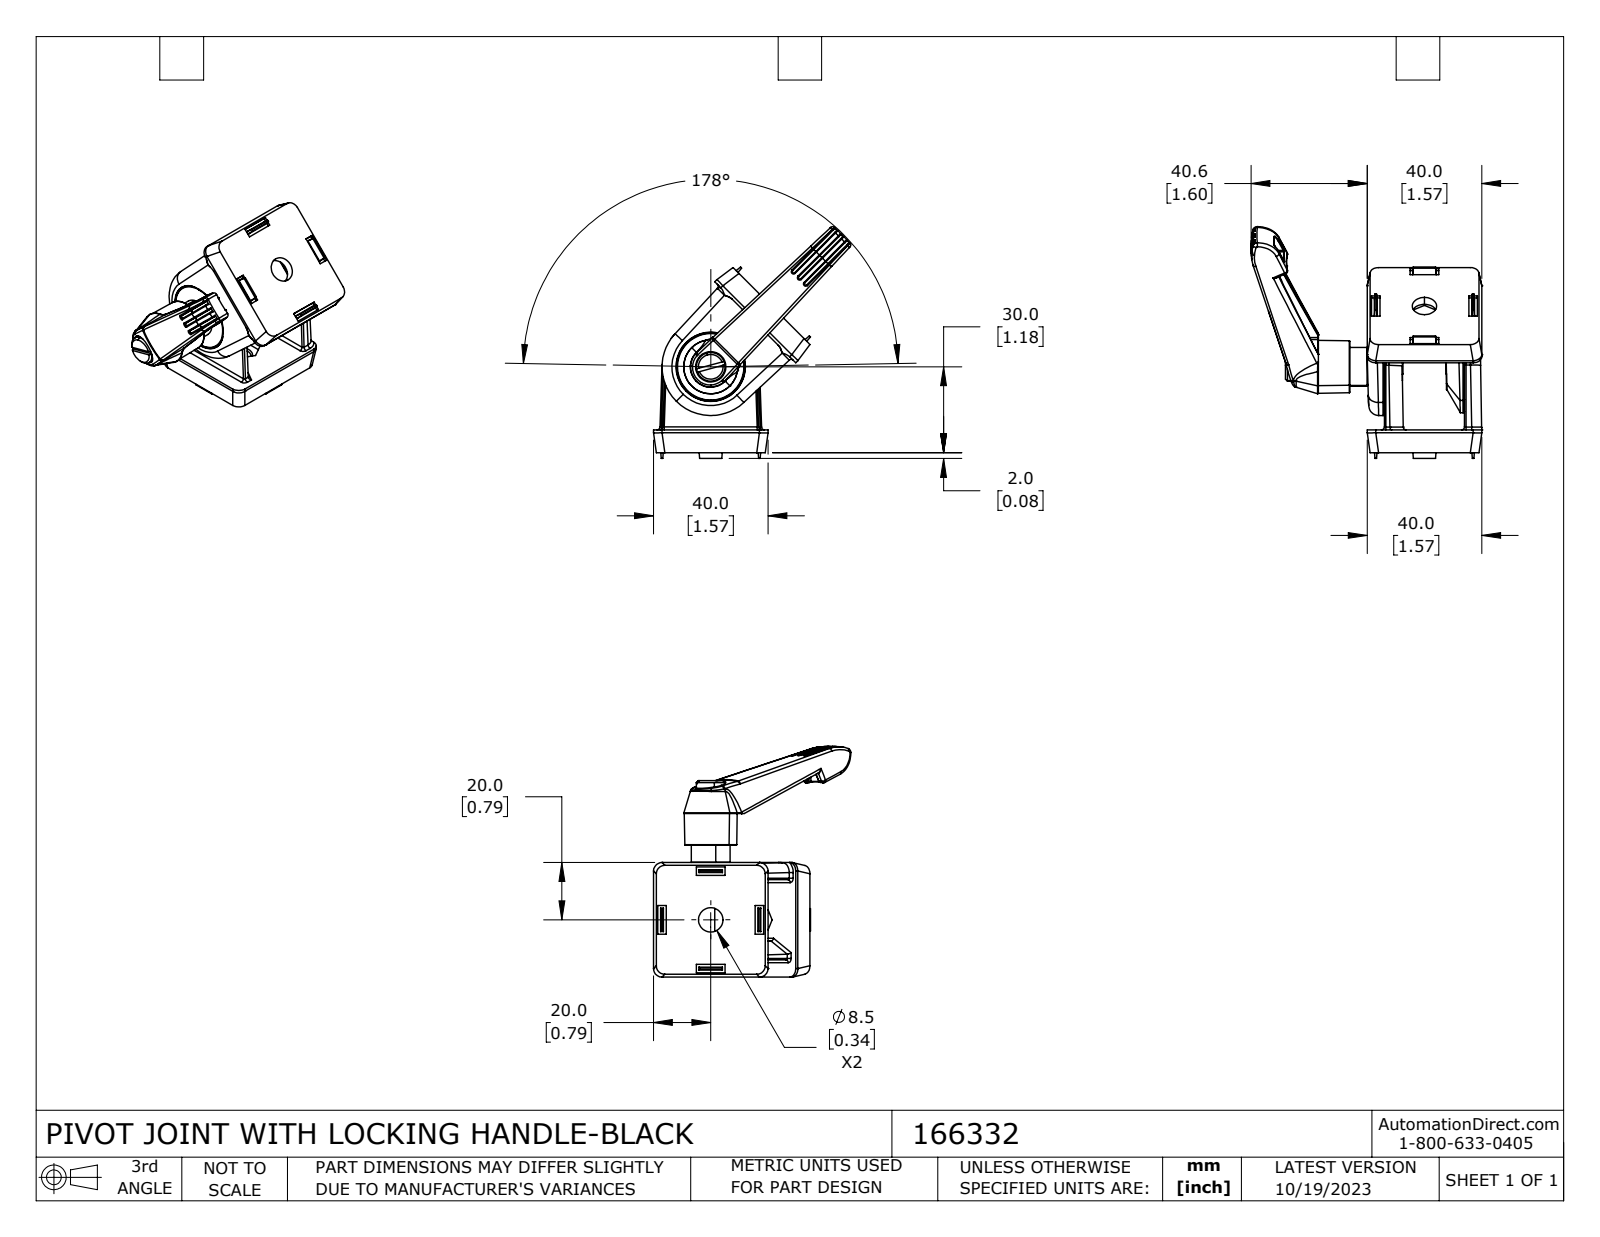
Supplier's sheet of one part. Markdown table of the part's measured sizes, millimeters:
| quantity | value |
| --- | --- |
| part name | 166332 |
| STEP written by | SolidWorks 2023 (CONFIG_CONTROL_DESIGN) |
| units | millimeters |
| bodies | 7 solids, 885 faces (256 planar, 205 cylindrical, 424 other) |
| overall size | 81.55 × 80.93 × 68.93 |
| volume | 55 135 mm³ |
| surface area | 29 501 mm² |
| round holes (diameter × count) | 2 × 4, 5 × 1, 5.6 × 1, 6.4 × 1, 10.6 × 1, 12.2 × 1, 13 × 1, 14 × 1, 24 × 1, 26 × 1 |
| round bosses / shafts (diameter × count) | 34 × 1, 32 × 1, 23.6 × 1, 16 × 1, 13.5 × 1, 12 × 1, 10 × 1, 6 × 1 |
| partial cylindrical surfaces (radius × count) | 0.2 × 45, 1 × 18, 3 × 16, 0.5 × 15, 0.3 × 4, 3.5 × 4, 4.6 × 1 |
| main face-to-face distances | 8, 28, 5.57, 33.57, 6.27, 32.87, 0.7, 27.3, 27.4, 4 |
| hole center spacings | 8.03, 10.49, 10.5, 19.4, 20.99, 21 |
